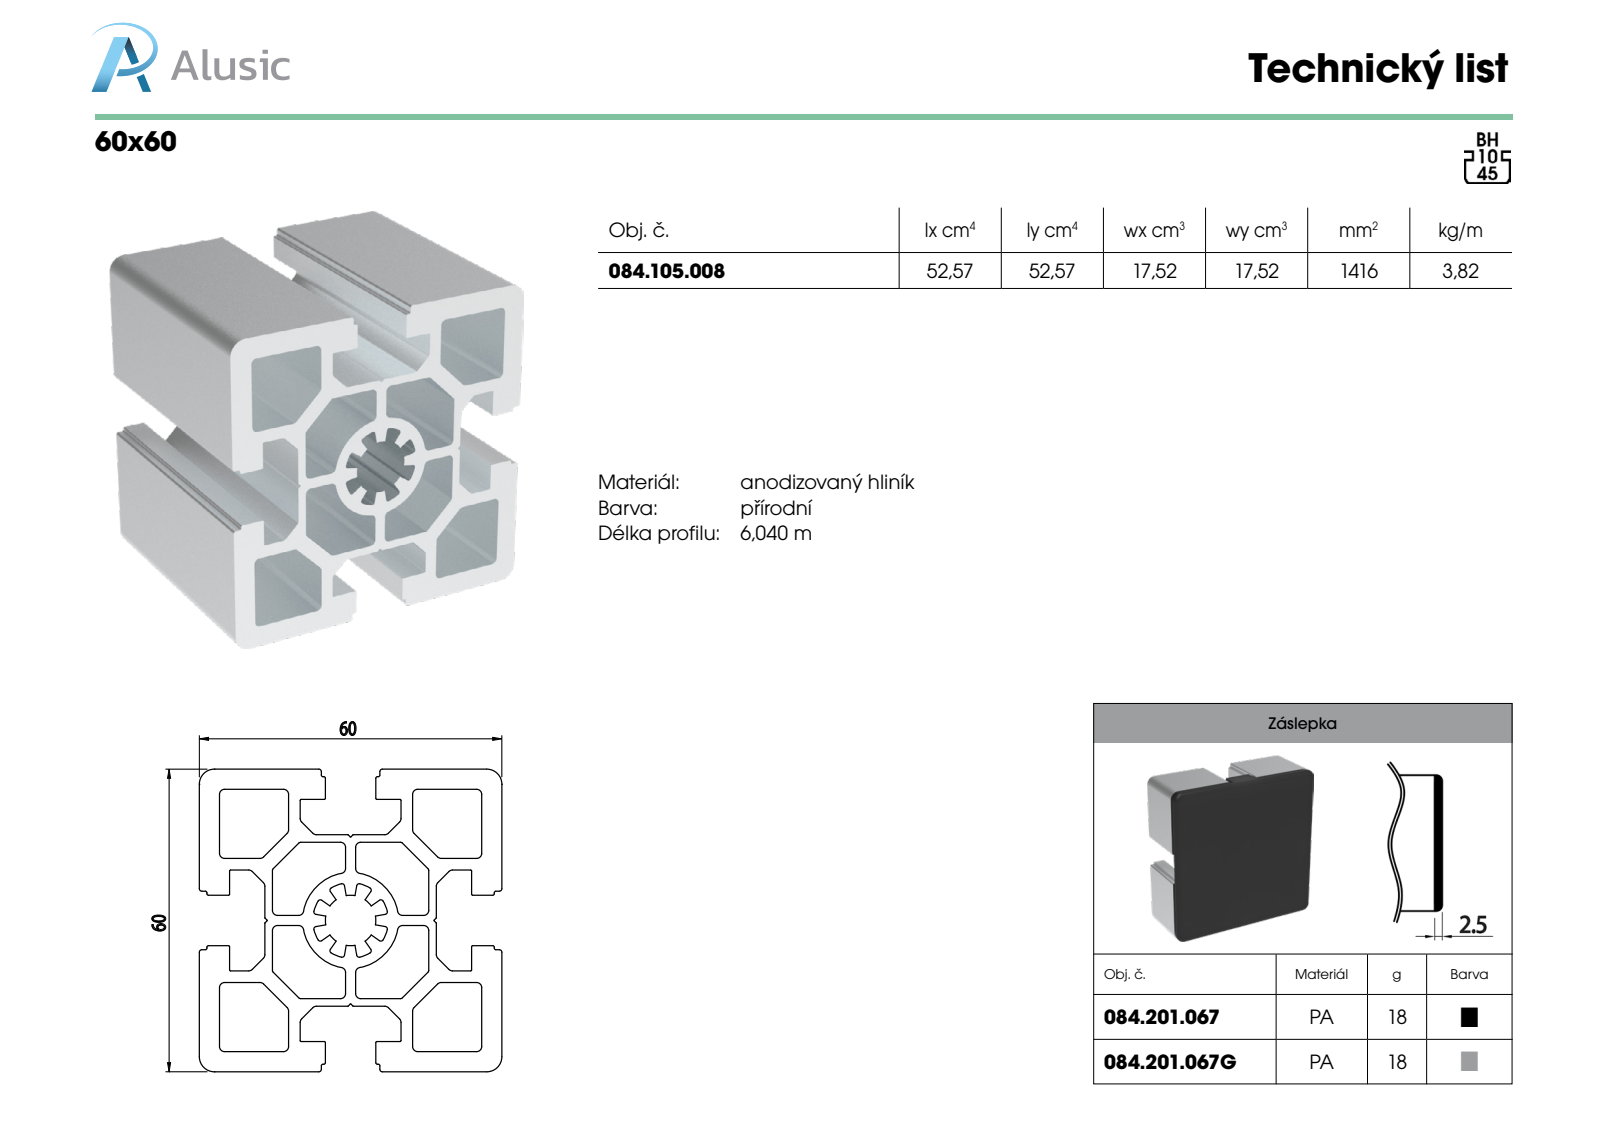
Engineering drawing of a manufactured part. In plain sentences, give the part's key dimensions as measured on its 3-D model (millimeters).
The part is named "084.201.067". Its 3-D file was written by "SolidWorks 2012 (CONFIG_CONTROL_DESIGN)". It is 1 solid with 84 faces: 64 planar, 12 cylindrical and 8 other. Overall it measures 60 by 60 by 10.5 millimeters. Its volume is 9 400 cubic millimeters and its surface area 8 171 square millimeters. Round holes: 1 of diameter 7.4. Round bosses or shafts: 1 of diameter 10.8. Partial cylindrical surfaces (rounded edges, fillets, slot ends): 4 of radius 2, 4 of radius 3. The main face-to-face distances are 2.5, 4, 60, 25.1, 34.9, 6, 8.5, 5.8, 2.7, 56.
